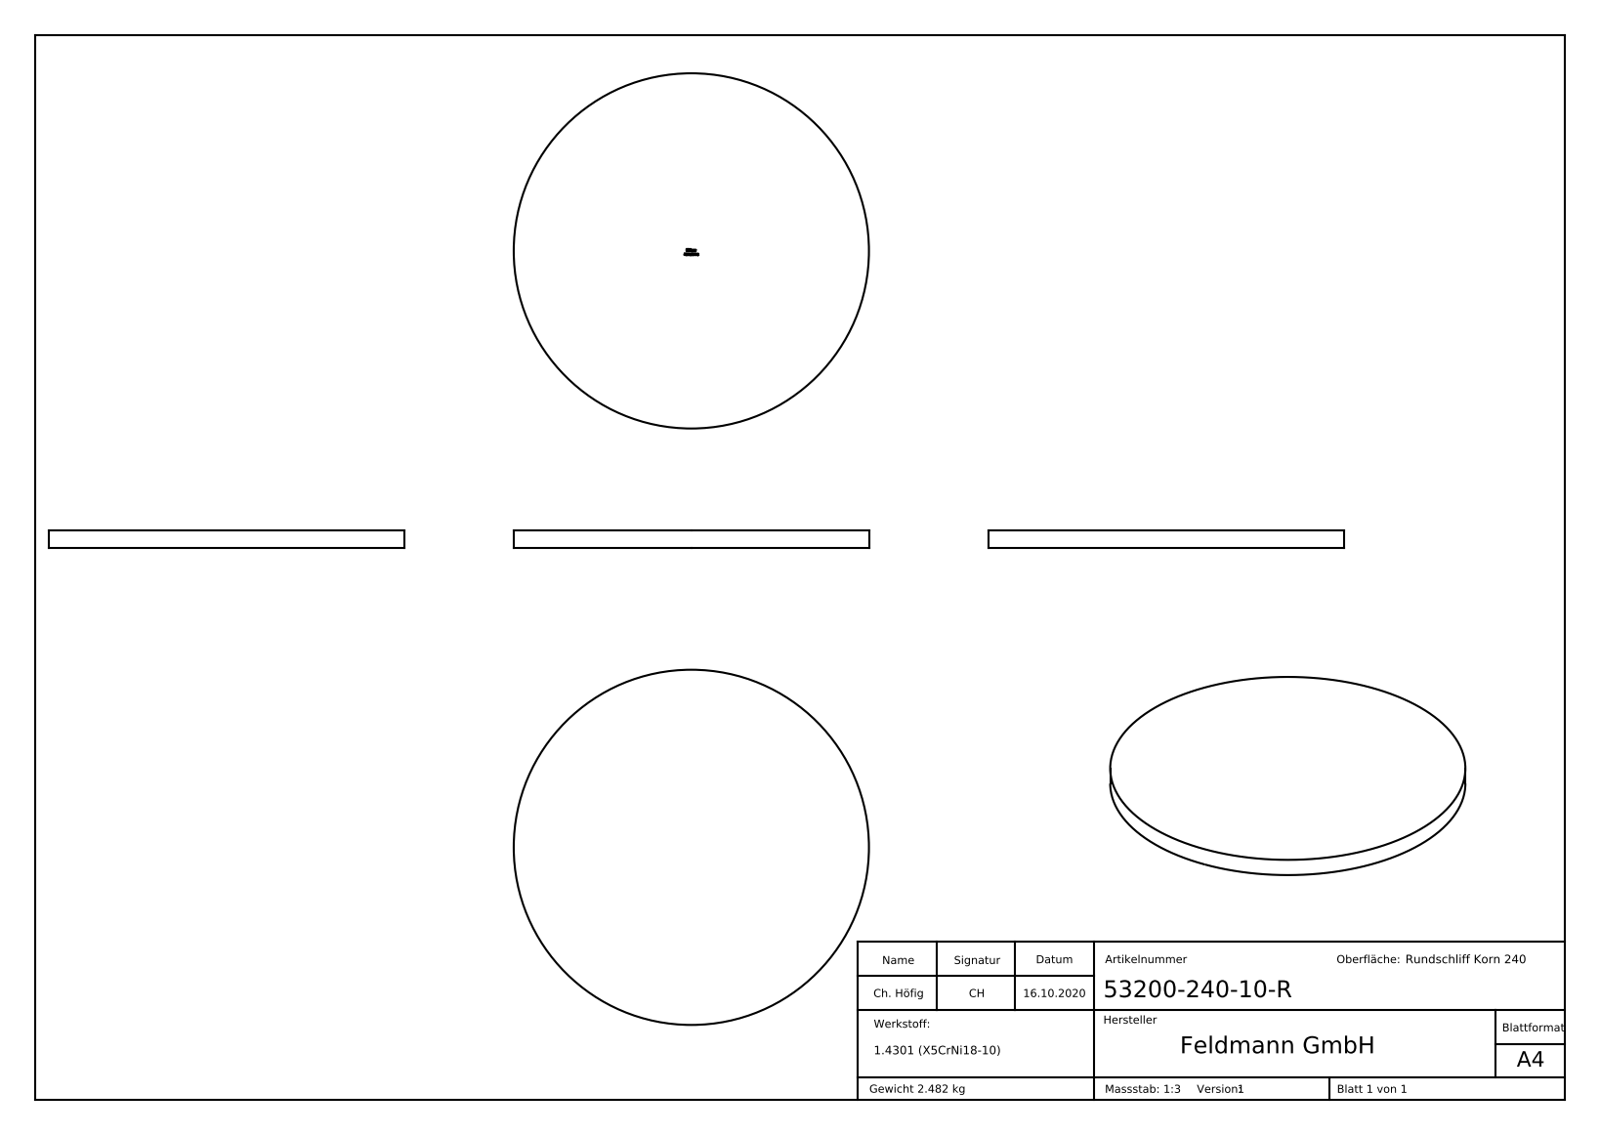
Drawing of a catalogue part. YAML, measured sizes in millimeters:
part_name: "53200-240-10-R"
step_written_by: "SolidWorks 2018 (CONFIG_CONTROL_DESIGN)"
units: millimeters
bodies: {solids: 1, faces: 275, planar: 150, cylindrical: 2, other: 123}
overall_size: [200, 200, 10]
volume: 314159
surface_area: 69122
round_bosses_or_shafts:
  - {diameter: 200, count: 1}
face_to_face_distances: [10, 9.9, 2.32, 1.78, 1.96, 1.53, 0.83, 1.86, 2.56, 2.77]
